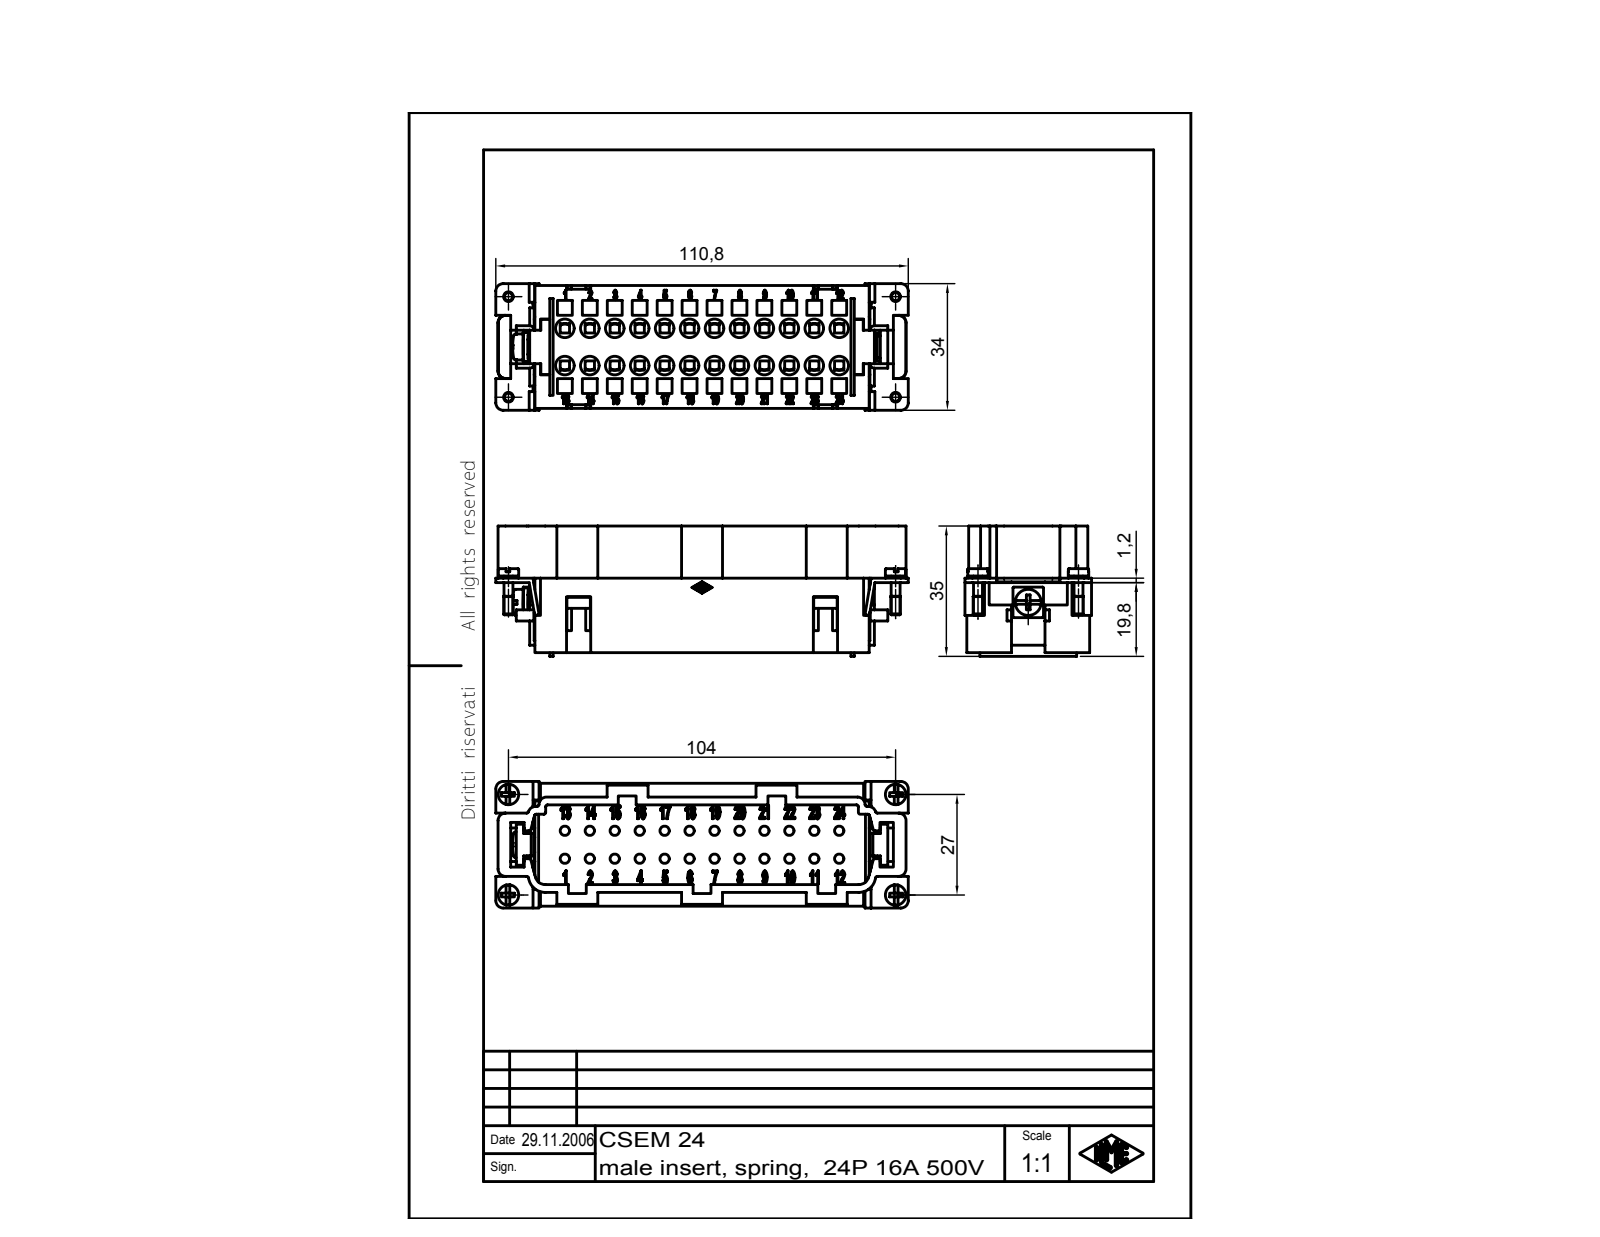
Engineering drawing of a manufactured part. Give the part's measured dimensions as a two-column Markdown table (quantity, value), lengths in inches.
| quantity | value |
| --- | --- |
| part name | CSEM Kontakteinsätze mit Käfigzugfederanschluss |
| STEP written by | Autodesk Inventor 7 (AUTOMOTIVE_DESIGN) |
| units | inches |
| bodies | 1 solid, 2133 faces (876 planar, 196 cylindrical, 1061 other) |
| overall size | 4.362 × 1.378 × 1.339 |
| volume | 4.053 in³ |
| surface area | 50.31 in² |
| round holes (diameter × count) | 0.197 × 12, 0.128 × 1 |
| round bosses / shafts (diameter × count) | 0.098 × 24, 0.217 × 2, 0.213 × 2, 0.102 × 2, 0.094 × 2, 0.276 × 1, 0.157 × 1 |
| partial cylindrical surfaces (radius × count) | 0.094 × 24, 0.004 × 14, 0.079 × 10, 0.02 × 6, 0.049 × 2, 0.008 × 1, 0.047 × 1, 0.054 × 1 |
| main face-to-face distances | 0.787, 1.071, 0.228, 1.154, 0.083, 1.299, 0.146, 0.925, 0.157, 0.843 |
| hole center spacings | 0.264, 0.528, 0.791, 1.055, 1.319, 1.583, 1.846, 2.11 |
